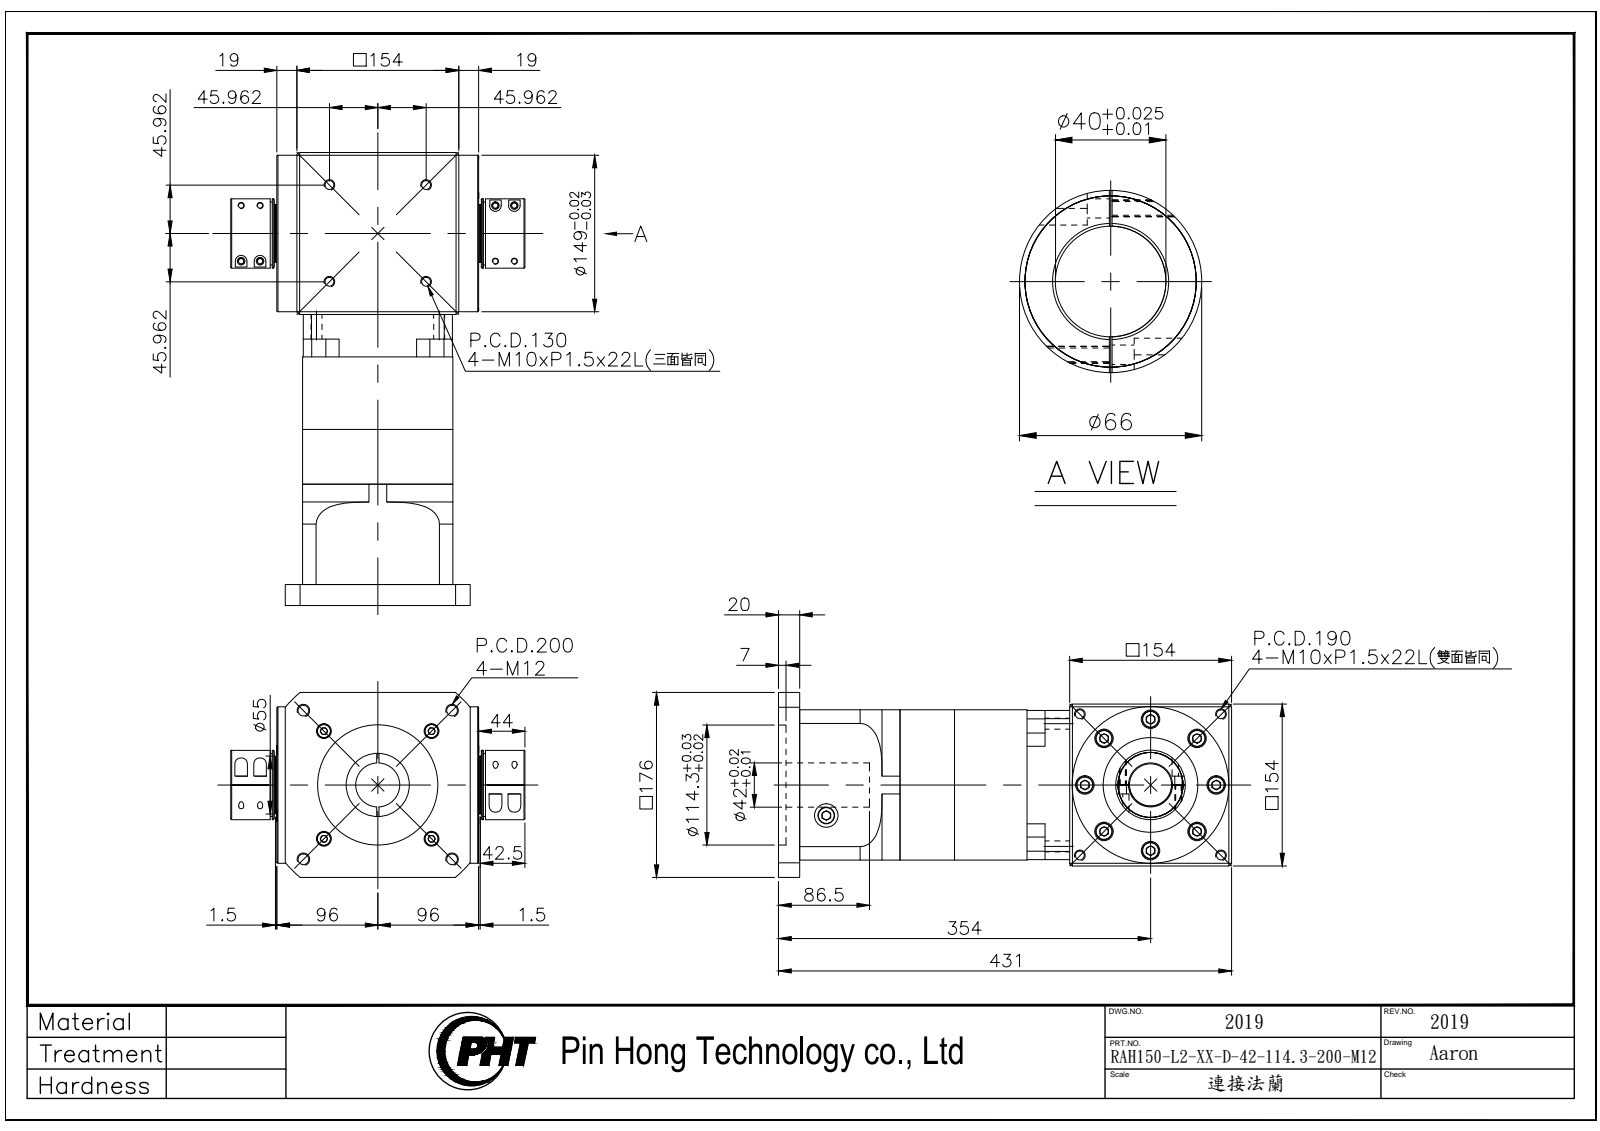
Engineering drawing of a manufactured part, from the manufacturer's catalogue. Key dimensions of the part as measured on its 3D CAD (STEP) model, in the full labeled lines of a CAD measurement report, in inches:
Part name (STEP PRODUCT): RAH150-L2-XX-D-42-114.3-200-M12_2019
STEP written by: SolidWorks 2016 (AUTOMOTIVE_DESIGN)
Units: inches
Bodies: 4 solids, 1362 faces (688 planar, 440 cylindrical, 234 other)
Overall size (bounding box): 16.969 × 11.024 × 6.929
Volume: 540.2 in³ · Surface area: 1 017 in²
Round holes (diameter × count): ⌀0.335 ×12, ⌀0.354 ×12, ⌀0.551 ×12, ⌀0.433 ×8, ⌀0.689 ×8, ⌀0.276 ×6, ⌀0.268 ×4, ⌀0.402 ×4, ⌀0.413 ×4, ⌀0.886 ×2, ⌀1.575 ×1, ⌀1.654 ×1
Round bosses / shafts (diameter × count): ⌀0.63 ×12, ⌀0.512 ×12, ⌀0.413 ×8, ⌀0.394 ×8, ⌀0.236 ×8, ⌀5.866 ×1, ⌀5.669 ×1, ⌀5.63 ×1
Partial cylindrical surfaces — rounded edges, fillets, slot ends (radius × count): R0.139 ×8, R0.217 ×8, R0.394 ×4, R3.15 ×1, R3.642 ×1, R3.74 ×1, R4.228 ×1, R4.528 ×1
Main face-to-face distances: 6.063, 0.217, 5.846, 6.594, 2.717, 4.311, 1.594, 7.657, 5.63, 10.374
Hole centre spacings: 2.598, 0.674, 0.756, 0.999, 1.578, 1.883, 2.651, 3.14
